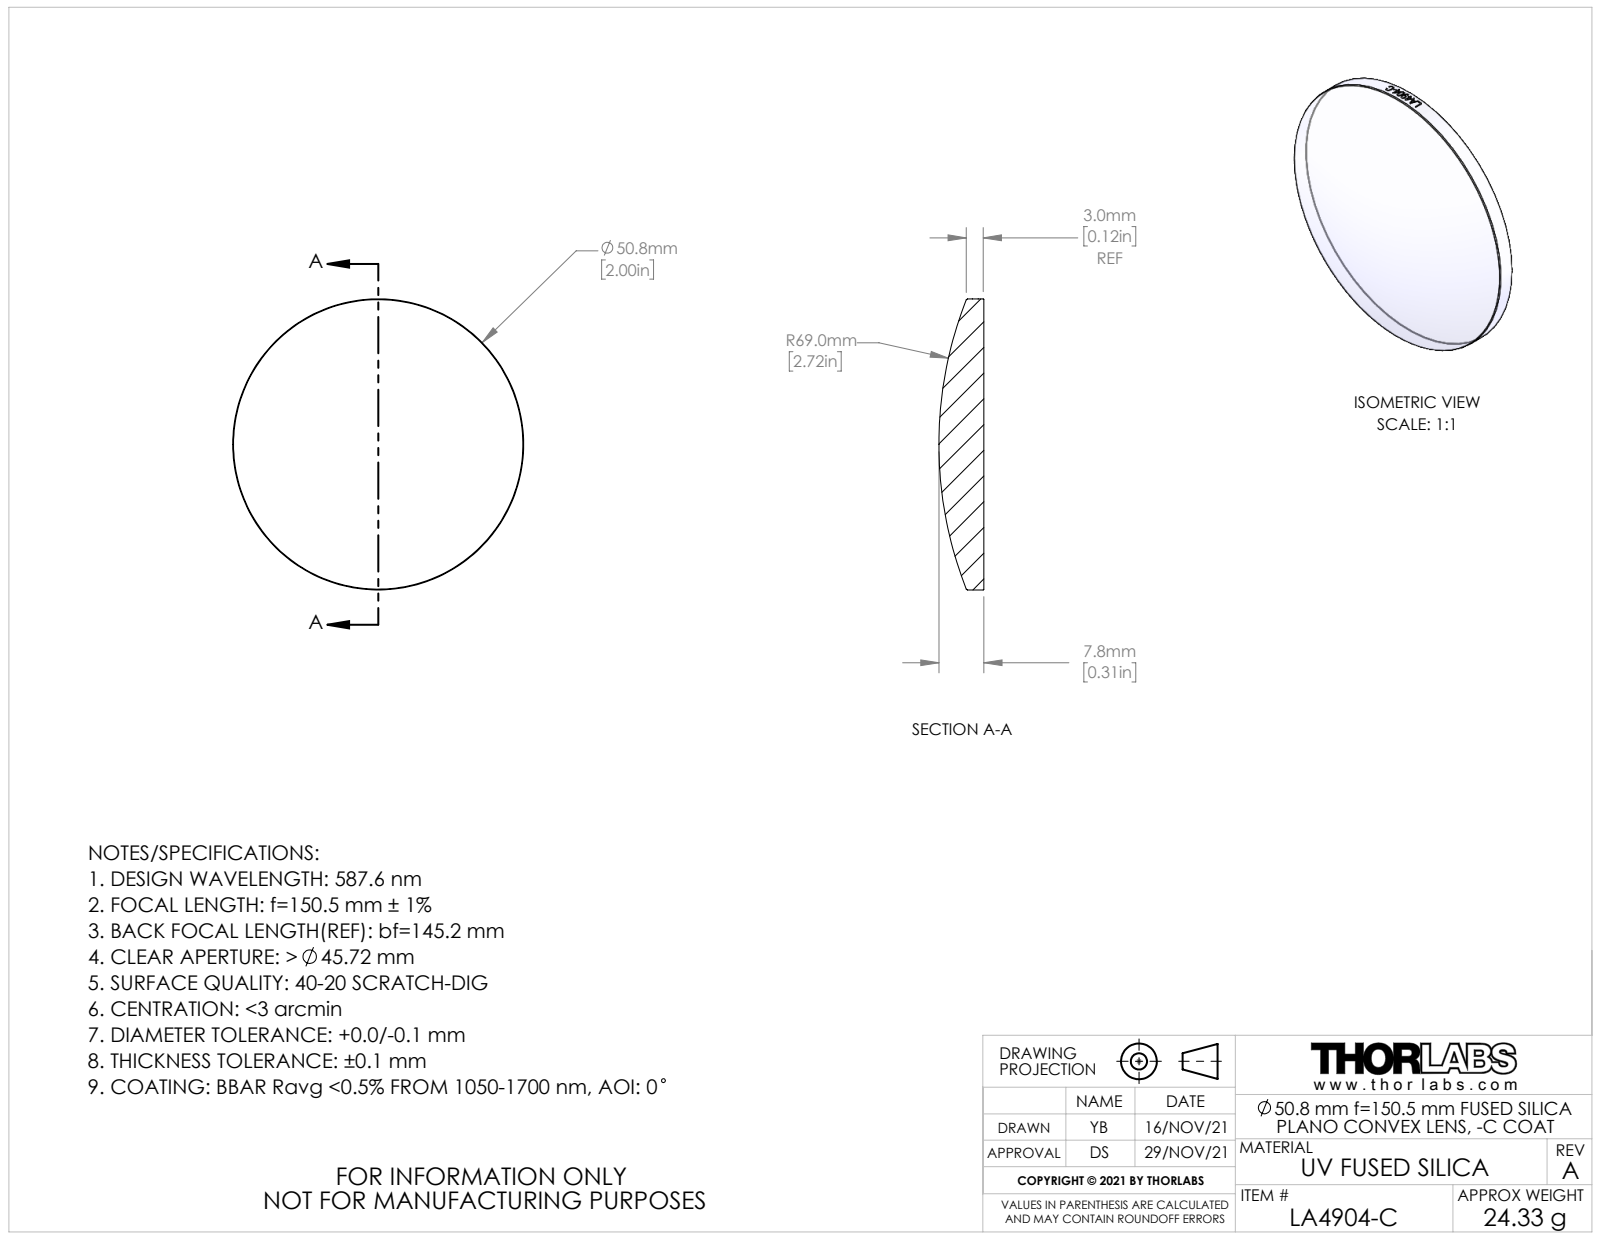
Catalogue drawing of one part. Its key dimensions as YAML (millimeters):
part_name: "CTN018144; CTN018075-E0W"
step_written_by: "SolidWorks 2018 (AUTOMOTIVE_DESIGN)"
units: millimeters
bodies: {solids: 1, faces: 22, planar: 1, cylindrical: 15, other: 6}
overall_size: [50.8, 50.8, 7.84]
volume: 11043
surface_area: 4588
round_bosses_or_shafts:
  - {diameter: 50.8, count: 1}
